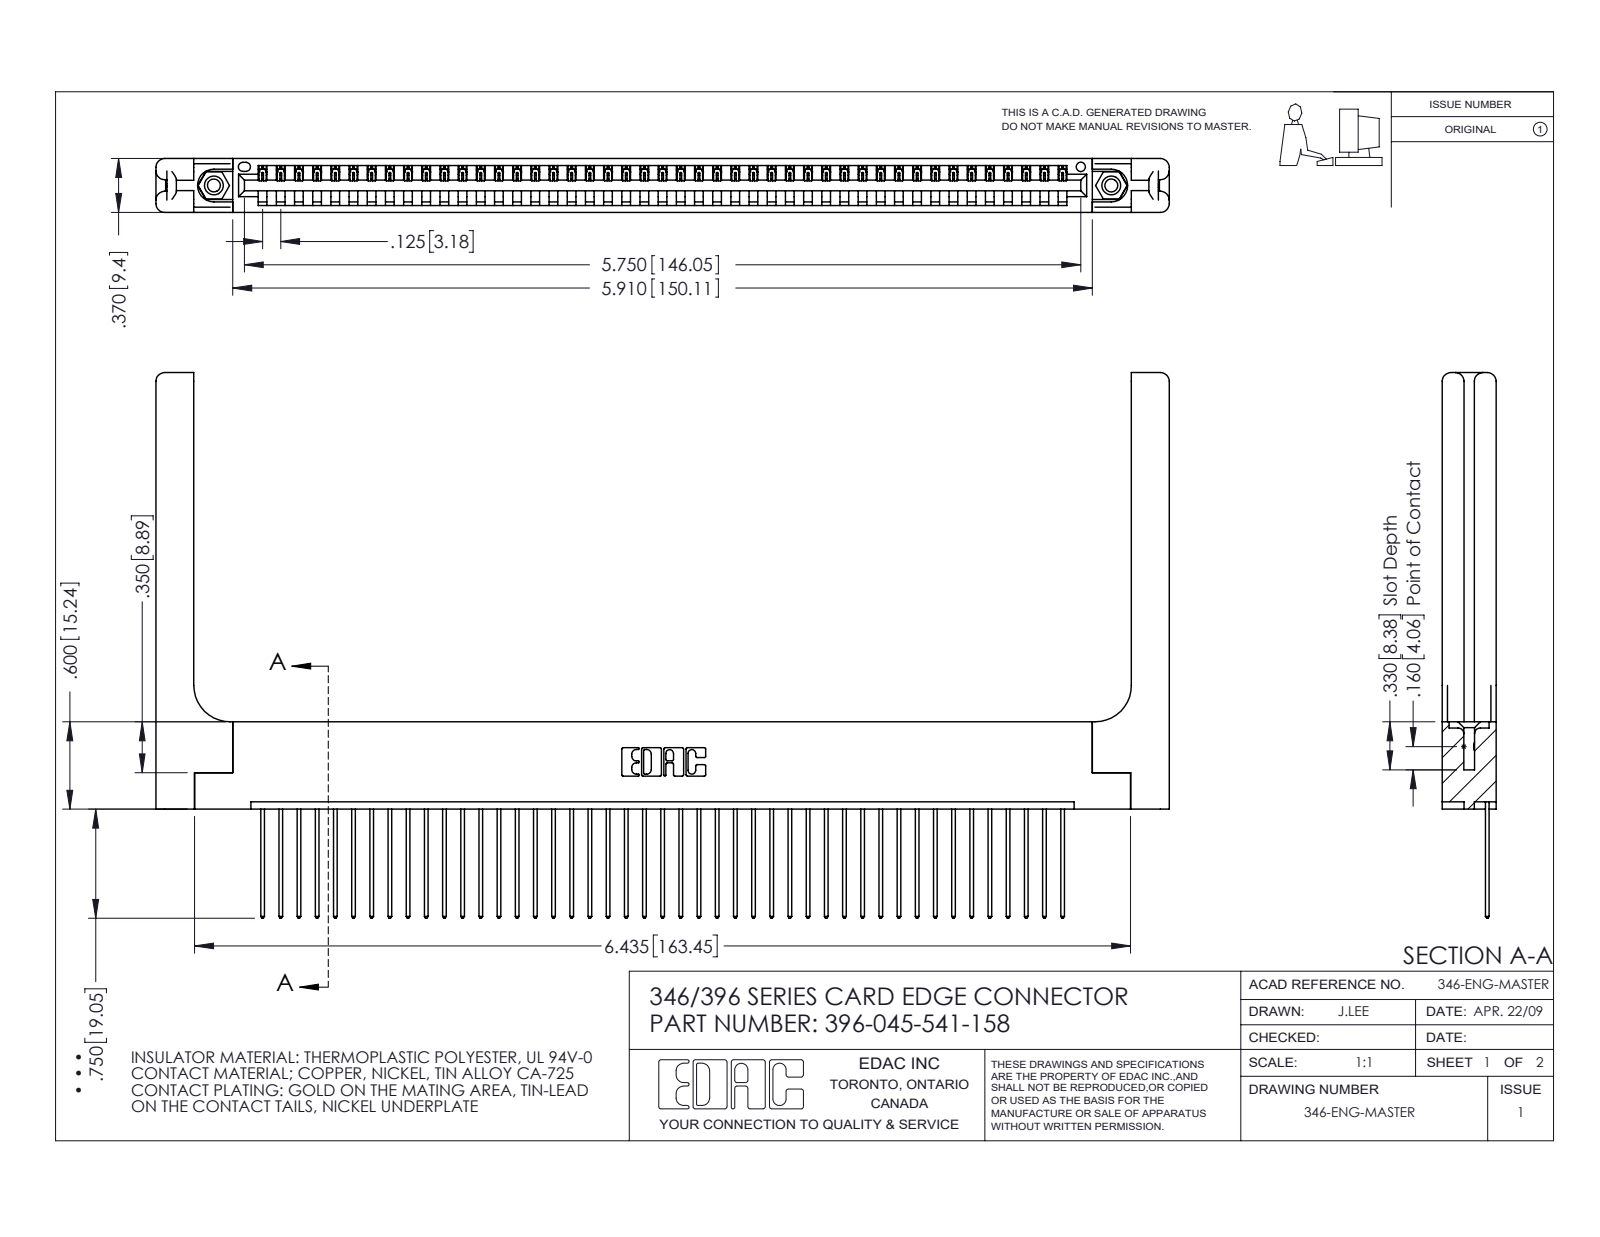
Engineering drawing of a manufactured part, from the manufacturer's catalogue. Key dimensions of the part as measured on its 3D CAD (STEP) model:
Part name (STEP PRODUCT): 396-045-541-158; 346-220-058_345-220-058; 346 Part_Flush Mounting Lugs - 0.156 Dia-TH; 345-250-001_345-250-001-102 (+1 more)
STEP written by: SolidWorks 2016 (CONFIG_CONTROL_DESIGN)
Units: inches
Bodies: 50 solids, 2988 faces (2024 planar, 904 cylindrical, 60 other)
Overall size (bounding box): 6.966 × 3.75 × 0.37
Volume: 1.503 in³ · Surface area: 42.58 in²
Round holes (diameter × count): ⌀0.089 ×2, ⌀0.125 ×2, ⌀0.156 ×2, ⌀0.064 ×1
Round bosses / shafts (diameter × count): ⌀0.155 ×2
Partial cylindrical surfaces — rounded edges, fillets, slot ends (radius × count): R0.006 ×90, R0.01 ×90, R0.01 ×22, R0.06 ×16, R0.007 ×6, R0.031 ×6, R0.026 ×3, R0.03 ×2
Main face-to-face distances: 0.37, 0.048, 0.322, 0.072, 0.148, 0.15, 0.298, 0.025, 0.25, 0.222
Hole centre spacings: 0.246, 5.961, 6.17
